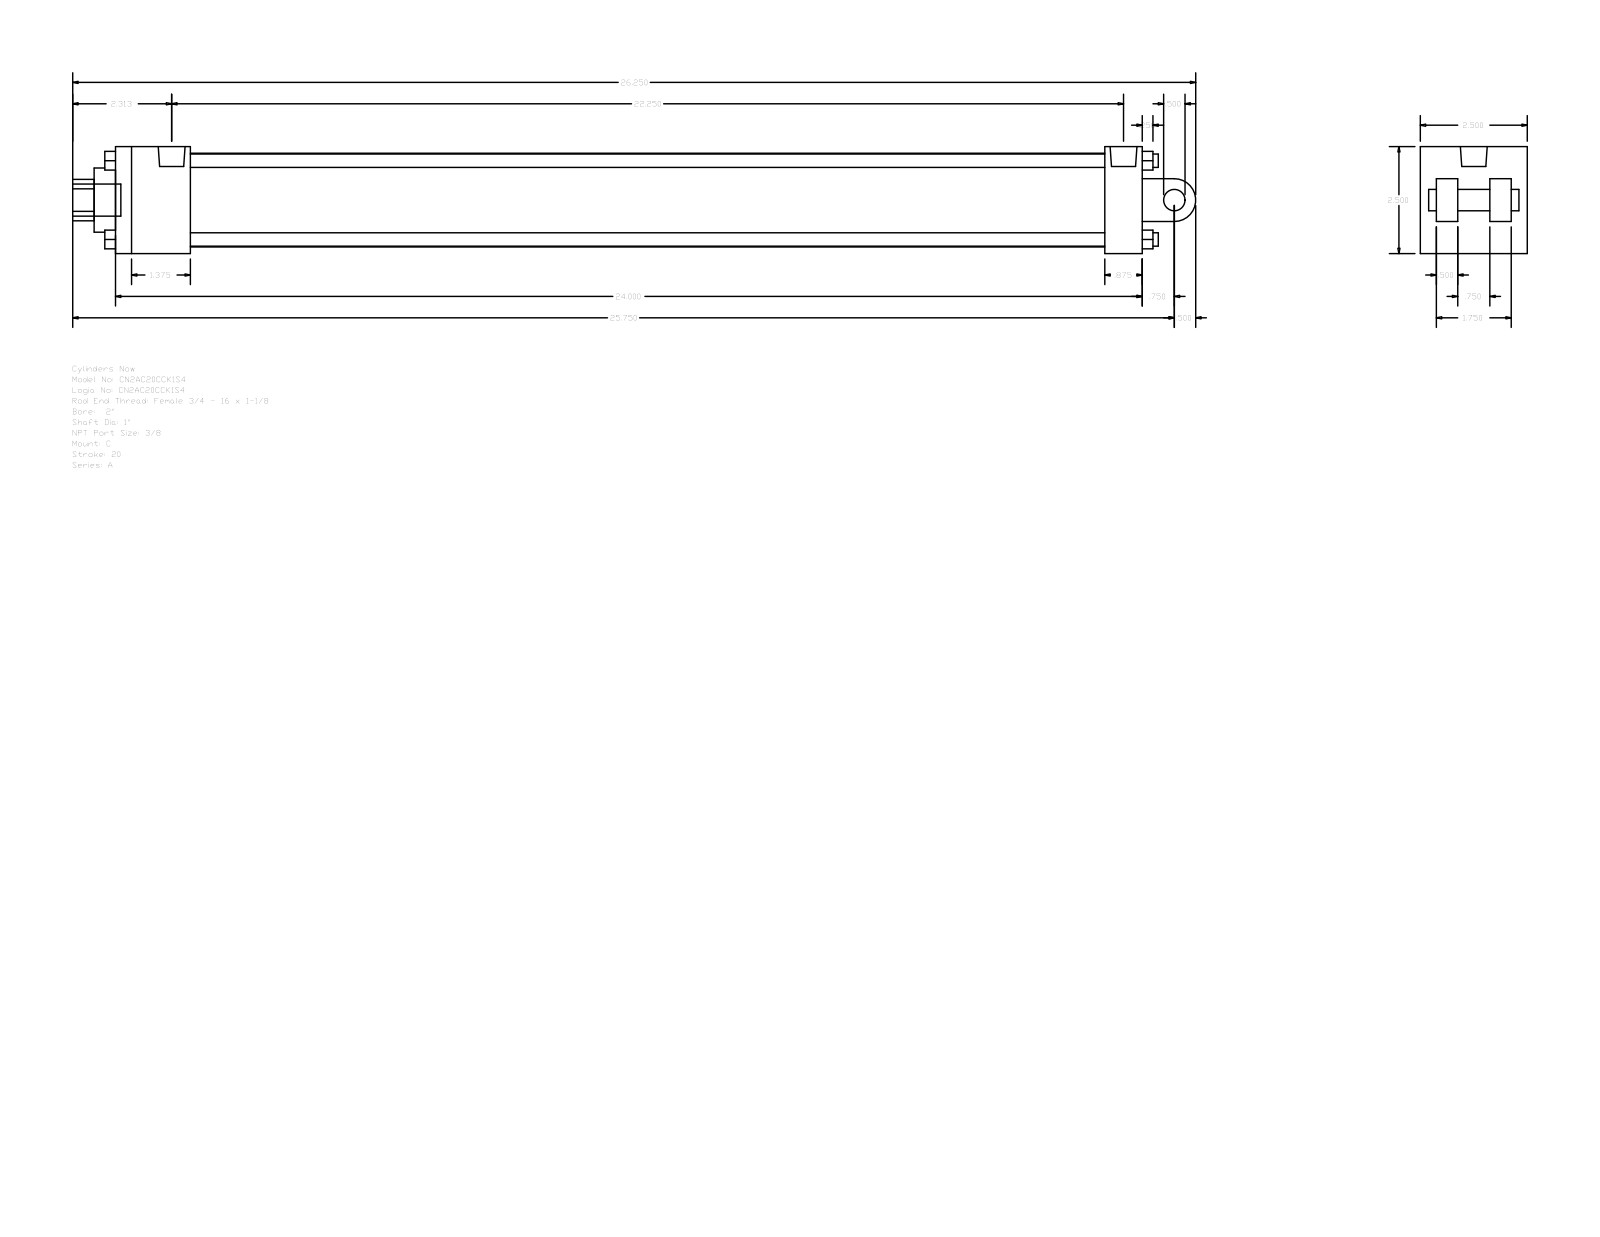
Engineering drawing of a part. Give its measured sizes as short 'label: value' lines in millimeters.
name: A_C__0200_1
written by: GSSL Pune (CONFIG_CONTROL_DESIGN)
unit: mm
bodies: 0 solids, 135 faces (102 planar, 33 cylindrical, 0 other)
size: 666.75 × 63.5 × 63.5
holes: 2× ⌀5.56, 1× ⌀15.93, 1× ⌀25.4, 1× ⌀38.1, 1× ⌀55.63
bosses: 4× ⌀7.94, 2× ⌀5.56, 1× ⌀19.05, 1× ⌀15.93, 1× ⌀12.7
rounds: 1× R12.29, 1× R12.7
face distances: 63.5, 609.6, 44.45, 12.7, 9.52, 41.28, 565.15, 587.37, 542.92, 22.23
hole spacings: 3.98
